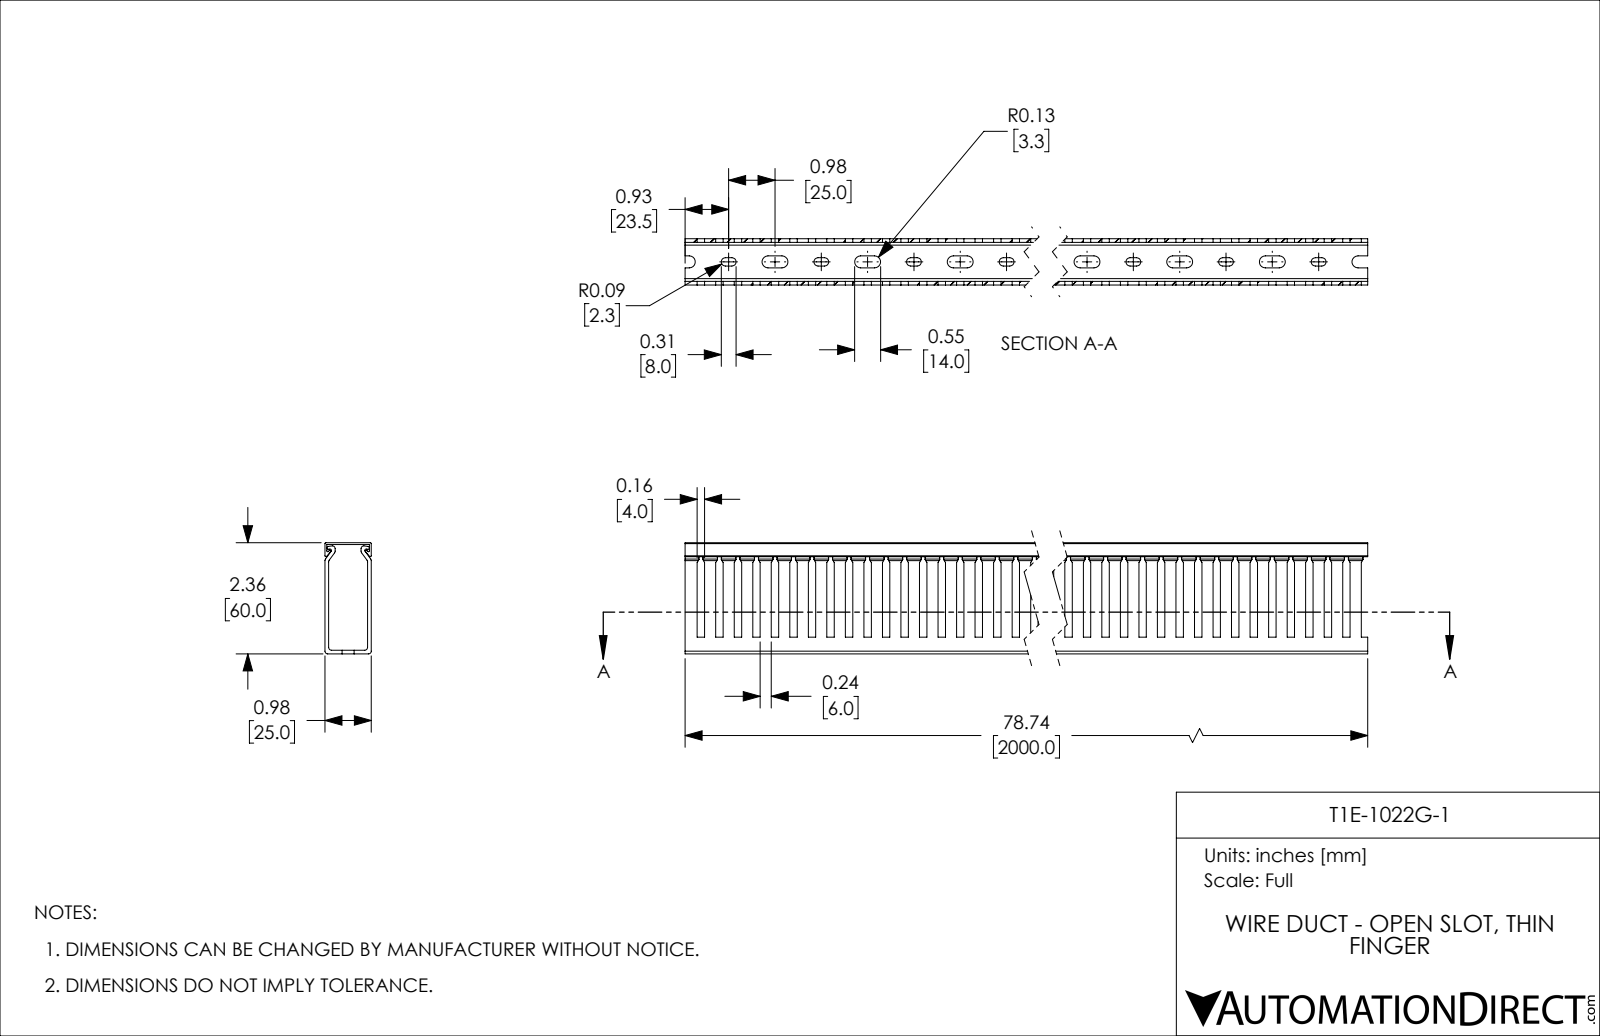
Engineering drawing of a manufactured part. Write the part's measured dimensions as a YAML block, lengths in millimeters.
part_name: "T1E-1022G-1"
step_written_by: "SolidWorks 2021 (CONFIG_CONTROL_DESIGN)"
units: millimeters
bodies: {solids: 2, faces: 945, planar: 514, cylindrical: 431, other: 0}
overall_size: [2000, 60, 25]
volume: 643609
surface_area: 735334
partial_cylinders:
  - {radius: 2.25, count: 80}
  - {radius: 3.25, count: 80}
  - {radius: 1.5, count: 12}
  - {radius: 0.5, count: 8}
  - {radius: 0.75, count: 6}
face_to_face_distances: [2, 23, 25, 21, 1, 60, 59, 57, 58, 24]
